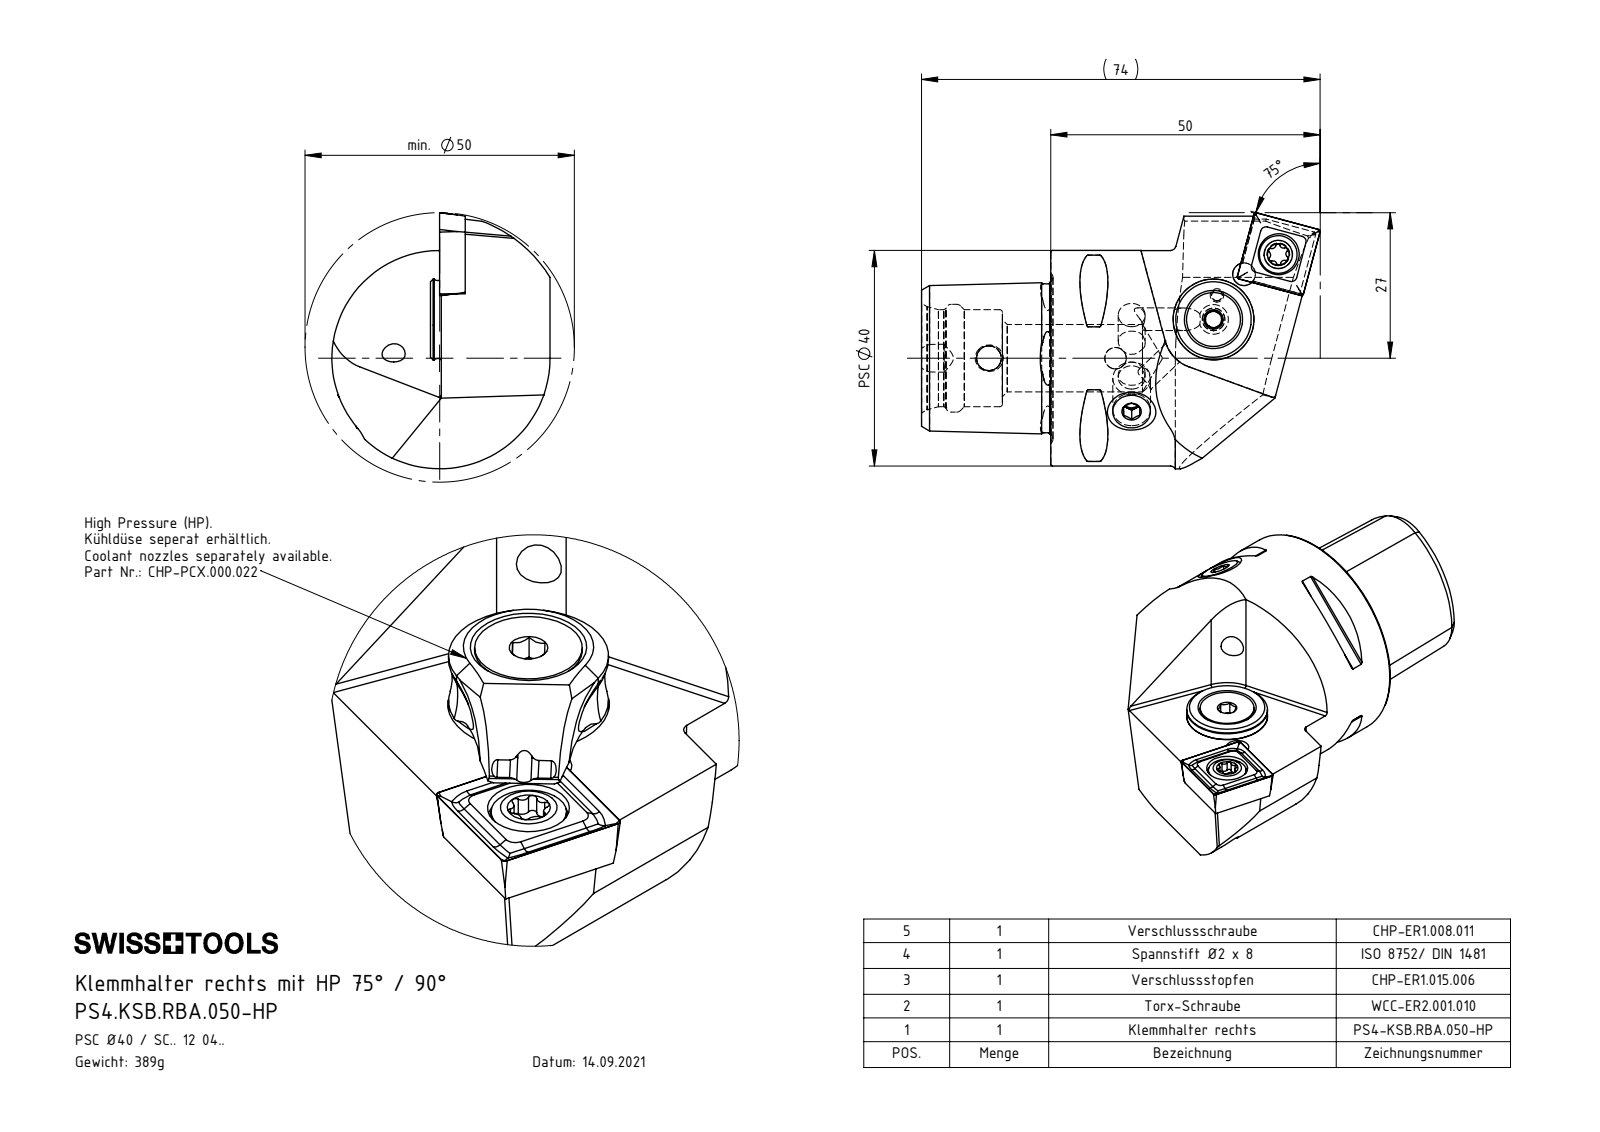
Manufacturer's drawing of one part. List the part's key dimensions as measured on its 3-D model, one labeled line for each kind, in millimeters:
Part name (STEP PRODUCT): ISO 8752 2x8; CHP-ER1.015.006; DIN 3771 - 13x1; CHP-ER1.008.011_A (+6 more)
STEP written by: SolidWorks 2022 (CONFIG_CONTROL_DESIGN)
Units: millimetres
Bodies: 8 solids, 383 faces (89 planar, 99 cylindrical, 195 other)
Overall size (bounding box): 74 × 47.5 × 40.5
Volume: 49 943 mm³ · Surface area: 15 579 mm²
Round holes (diameter × count): ⌀4.2 ×5, ⌀1.2 ×1, ⌀2 ×1, ⌀2.5 ×1, ⌀3 ×1, ⌀4 ×1, ⌀4.6 ×1, ⌀5 ×1, ⌀5.2 ×1, ⌀5.5 ×1, ⌀7 ×1, ⌀7.6 ×1
Round bosses / shafts (diameter × count): ⌀5 ×2, ⌀40 ×1, ⌀15 ×1, ⌀13.4 ×1, ⌀10 ×1, ⌀8 ×1, ⌀7 ×1, ⌀5.5 ×1
Partial cylindrical surfaces — rounded edges, fillets, slot ends (radius × count): R0.3 ×8, R0.39 ×6, R0.69 ×6, R0.5 ×2, R3 ×1, R7 ×1, R20.5 ×1, R25 ×1
Main face-to-face distances: 20.2, 15.7, 4.5, 15.74, 4.46, 24, 15.52, 35.3, 15, 22.1
Hole centre spacings: 4.5, 6.38, 7.36, 7.45, 10.11, 13.7, 13.8, 17.03
